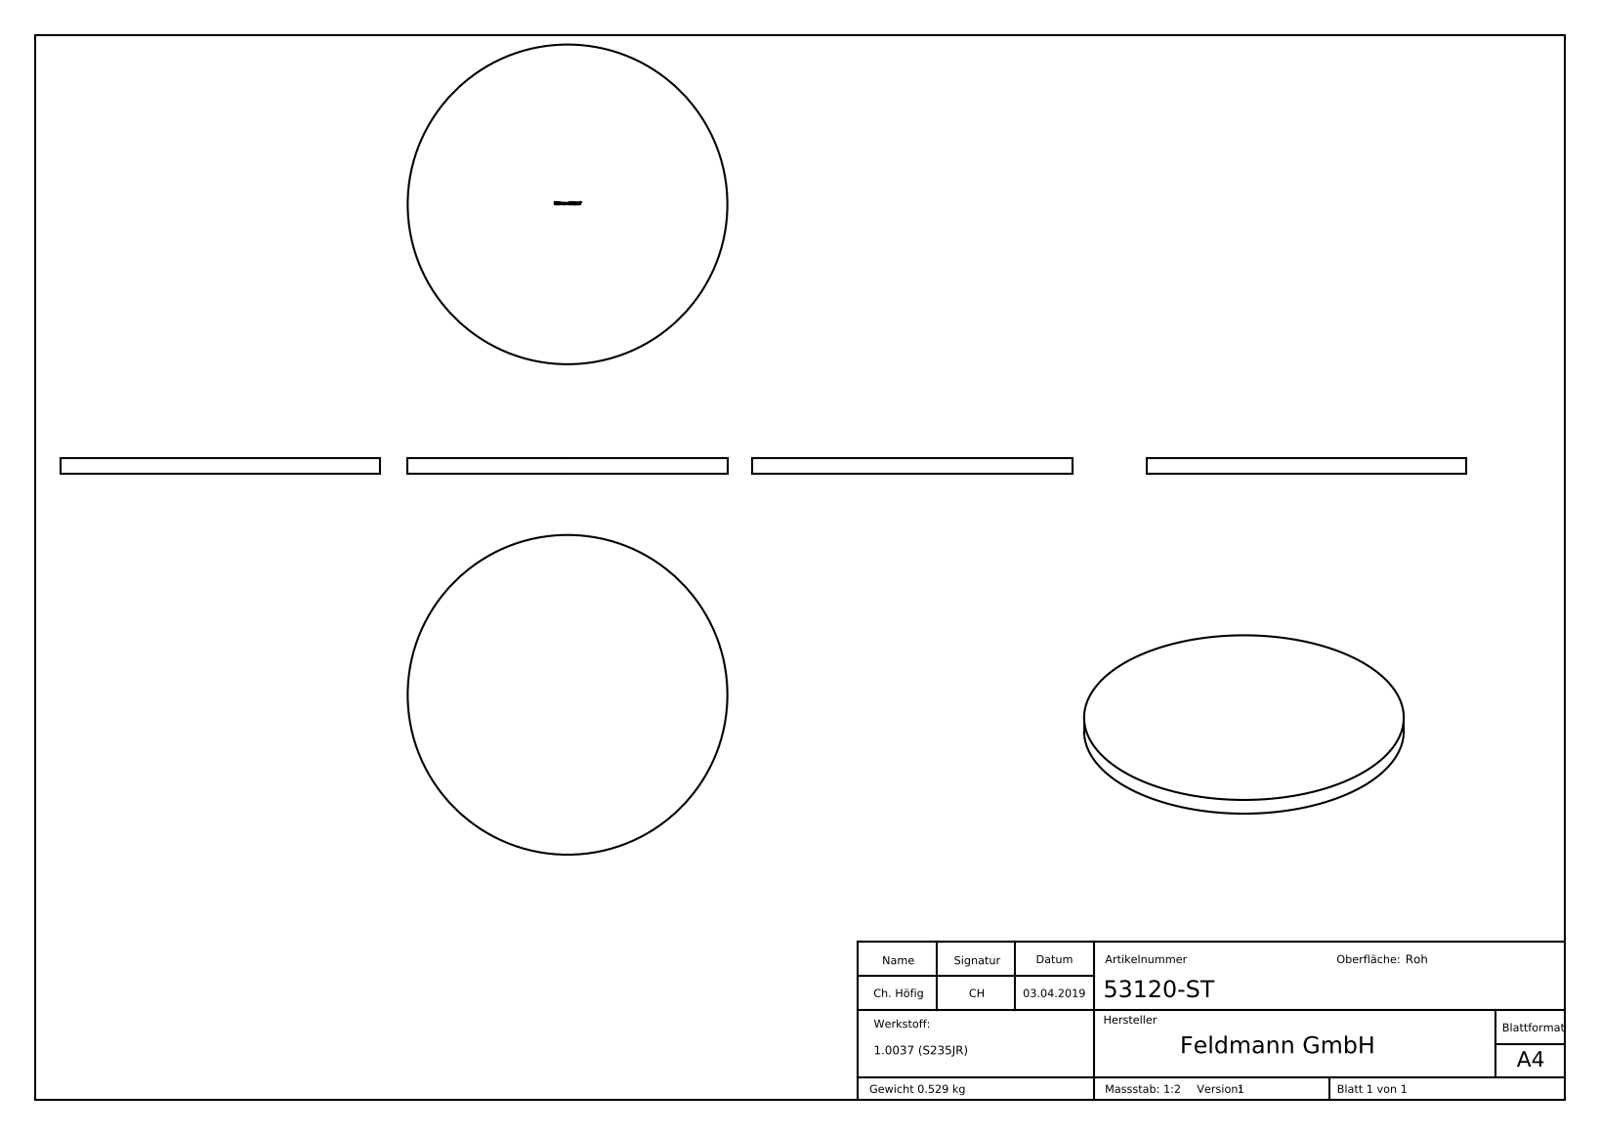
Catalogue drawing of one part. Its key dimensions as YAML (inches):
part_name: "53120-ST"
step_written_by: "SolidWorks 2015 (CONFIG_CONTROL_DESIGN)"
units: inches
bodies: {solids: 1, faces: 213, planar: 111, cylindrical: 2, other: 100}
overall_size: [4.724, 4.724, 0.236]
volume: 4.141
surface_area: 38.57
round_bosses_or_shafts:
  - {diameter: 4.724, count: 1}
face_to_face_distances: [0.236, 0.232, 0.031, 0.017, 0.039, 0.07, 0.23, 0.048, 0.334, 0.105]
